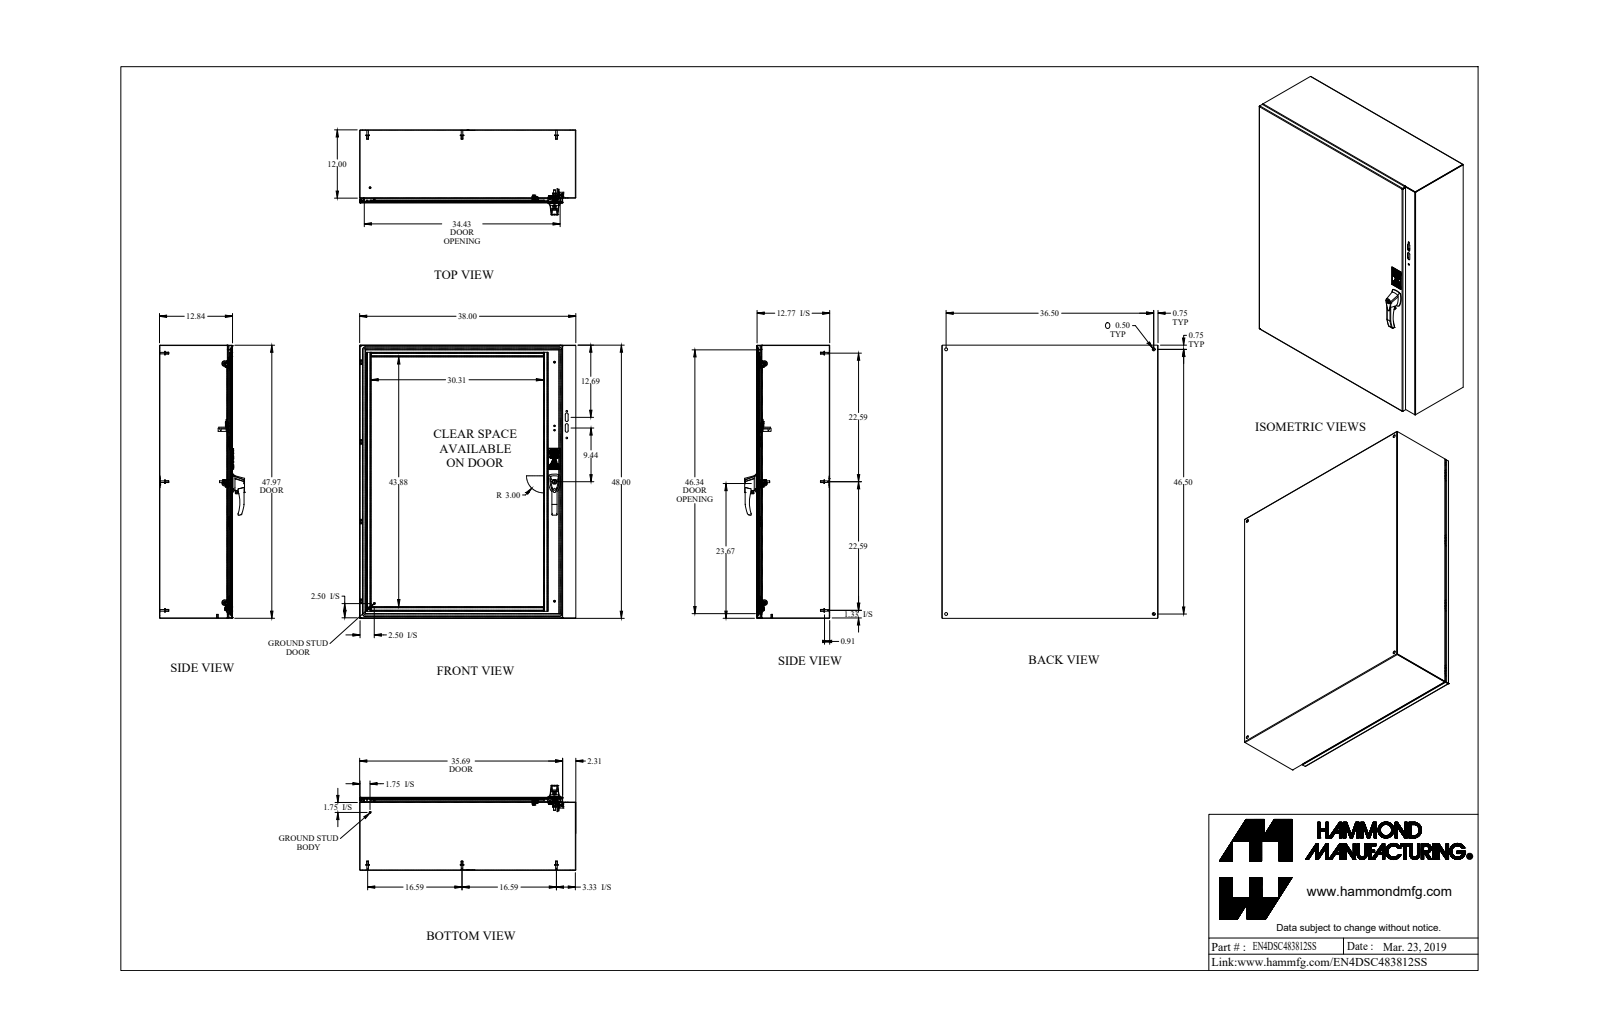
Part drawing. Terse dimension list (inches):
name: EN4DSC483812SS
written by: SolidWorks 2019 (AUTOMOTIVE_DESIGN)
unit: in
bodies: 75 solids, 1578 faces (889 planar, 476 cylindrical, 213 other)
size: 48 × 38 × 14.952
volume: 481.2 in³; area: 13 248 in²
holes: 6× ⌀0.176, 4× ⌀0.5, 3× ⌀0.196, 3× ⌀0.25, 3× ⌀0.265, 3× ⌀0.413, 2× ⌀0.156, 2× ⌀0.172, 2× ⌀0.173, 2× ⌀0.215, 2× ⌀0.256, 2× ⌀0.281
bosses: 9× ⌀0.25, 8× ⌀0.625, 8× ⌀0.313, 8× ⌀0.27, 6× ⌀0.156, 5× ⌀0.375, 3× ⌀1, 2× ⌀0.63
rounds: 24× R0.043, 24× R0.081, 18× R0.036, 18× R0.108, 17× R0.062, 15× R0.25, 14× R0.03, 14× R0.125
face distances: 0.072, 12.765, 12.693, 12.837, 37.928, 47.928, 37.856, 38, 47.856, 48
hole spacings: 21, 1.11, 2.883, 21, 21.001, 32.722, 36.5, 42.001
